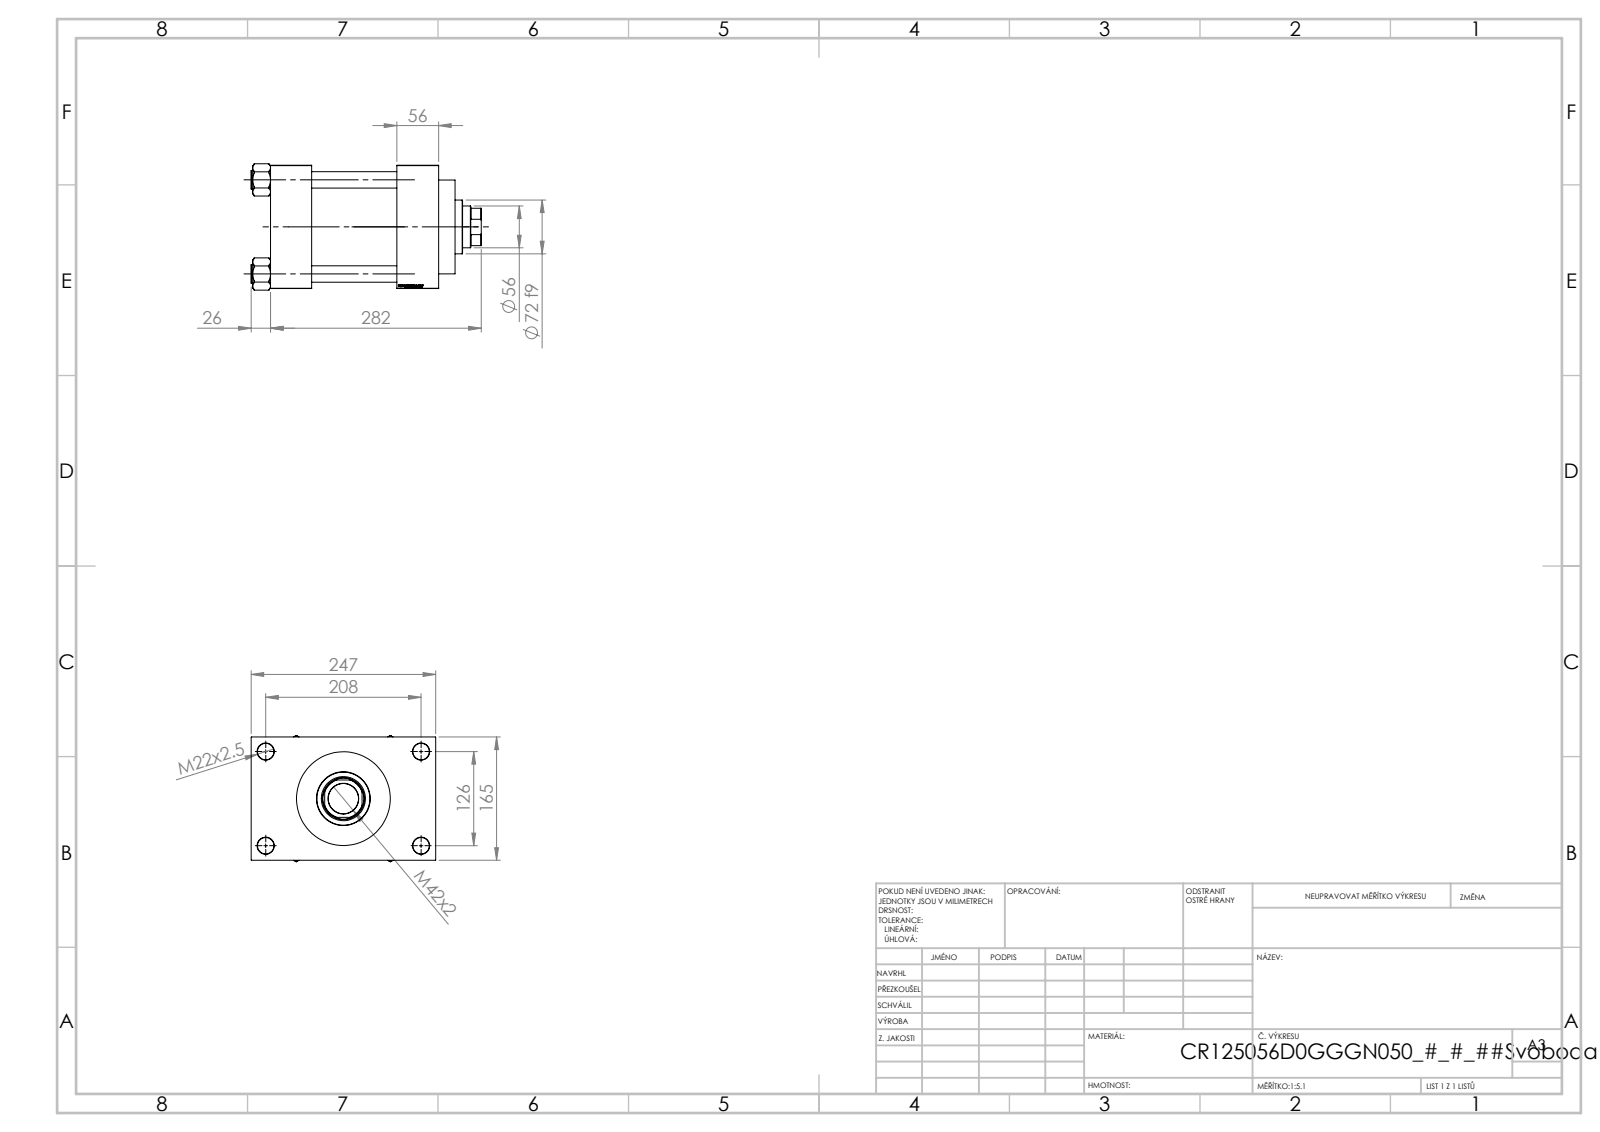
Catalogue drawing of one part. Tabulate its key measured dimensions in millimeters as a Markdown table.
| quantity | value |
| --- | --- |
| part name | V215_VC_A; V215CR_D_TYCINKA; V215CR_VCP_D; V215CR_D_Body (+1 more) |
| STEP written by | SolidWorks 2019 (CONFIG_CONTROL_DESIGN) |
| units | millimeters |
| bodies | 11 solids, 1149 faces (544 planar, 87 cylindrical, 518 other) |
| overall size | 308 × 247 × 169.14 |
| volume | 5 113 000 mm³ |
| surface area | 567 616 mm² |
| round holes (diameter × count) | 22 × 8, 7 × 2, 32.24 × 2, 45 × 2, 40.5 × 1, 56 × 1, 59 × 1, 96 × 1, 125 × 1, 125.5 × 1 |
| round bosses / shafts (diameter × count) | 25 × 4, 131 × 1, 72 × 1 |
| partial cylindrical surfaces (radius × count) | 27 × 1 |
| main face-to-face distances | 114, 165, 55, 169, 56, 225, 170, 41, 206, 247 |
| hole center spacings | 41.05, 89.02, 121.59, 125.9, 132.47, 166.95, 209.13, 126 |
